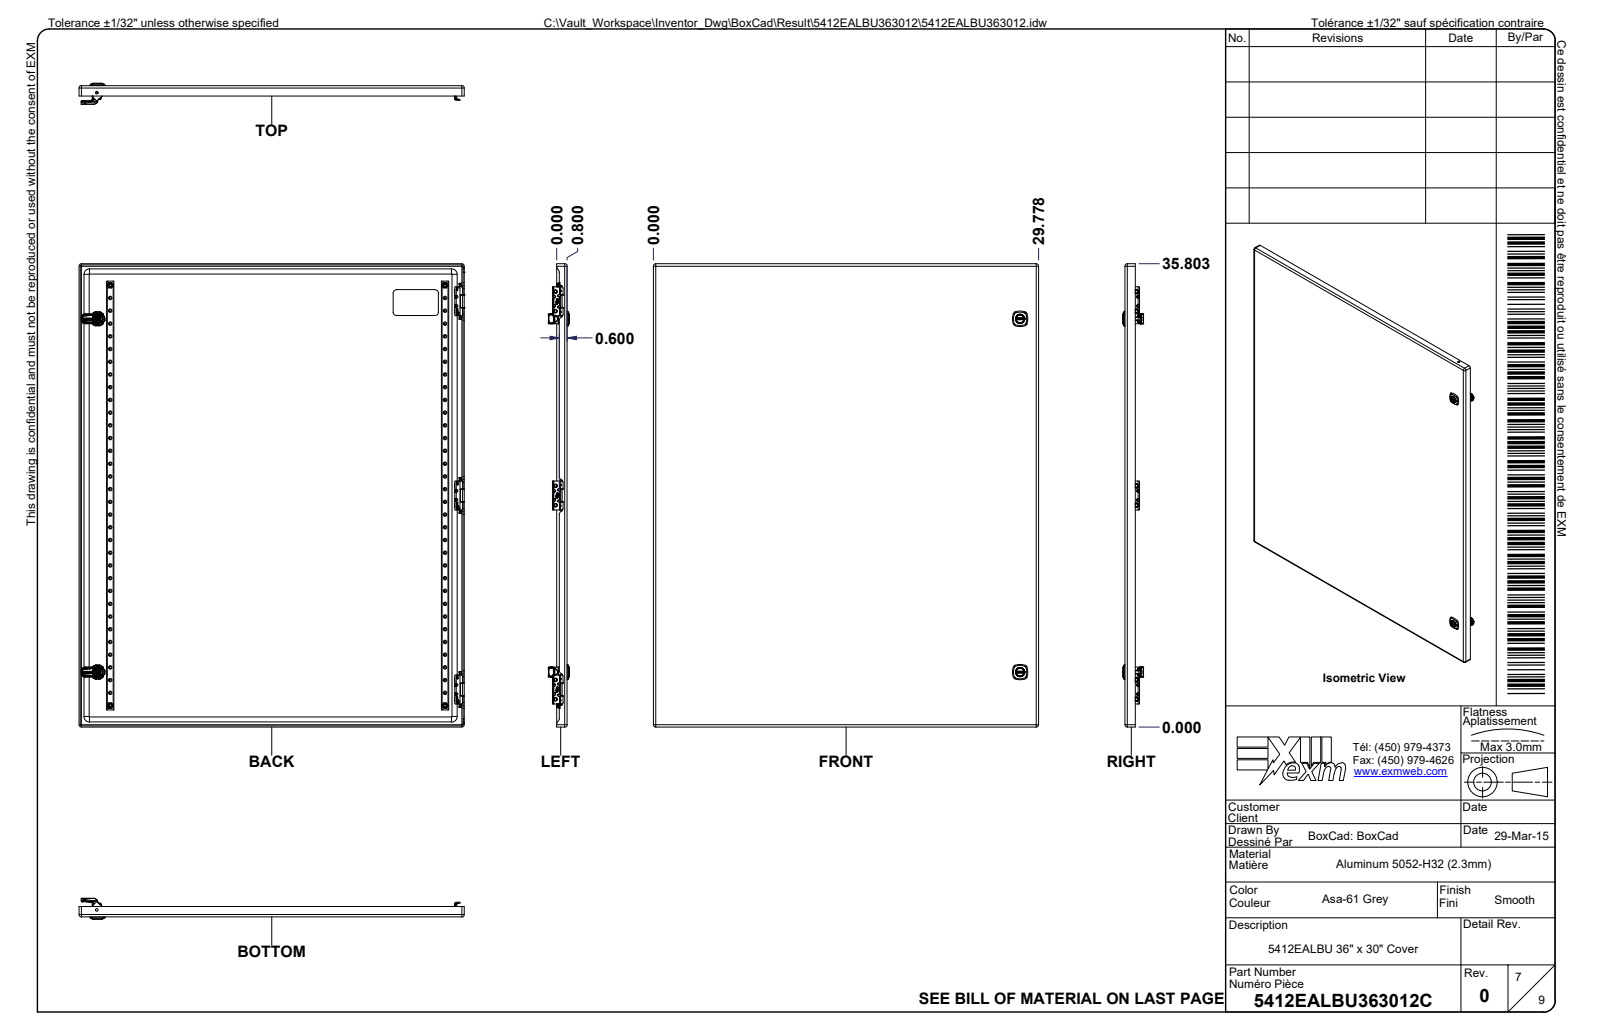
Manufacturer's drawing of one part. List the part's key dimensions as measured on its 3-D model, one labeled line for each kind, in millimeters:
Part name (STEP PRODUCT): 5412EALBU363012; 5412EALBU363012B; 5412EALBU363012B-P; STK-Q-16010 (+8 more)
STEP written by: Autodesk Inventor 2024 (AUTOMOTIVE_DESIGN)
Units: millimetres
Bodies: 87 solids, 7797 faces (3651 planar, 1605 cylindrical, 2541 other)
Overall size (bounding box): 914.4 × 762 × 338.7
Volume: 7 959 000 mm³ · Surface area: 6 833 000 mm²
Round holes (diameter × count): ⌀4.2 ×64, ⌀0.8 ×11, ⌀7.4 ×10, ⌀8 ×8, ⌀1.1 ×6, ⌀4.9 ×6, ⌀5.1 ×6, ⌀6 ×6, ⌀6.9 ×6, ⌀7.9 ×6, ⌀9 ×6, ⌀12.7 ×6
Round bosses / shafts (diameter × count): ⌀6 ×64, ⌀5.9 ×13, ⌀1 ×12, ⌀0.8 ×11, ⌀12 ×6, ⌀9 ×6, ⌀7.9 ×6, ⌀6.4 ×6
Partial cylindrical surfaces — rounded edges, fillets, slot ends (radius × count): R0.2 ×140, R0.5 ×106, R1 ×94, R0.3 ×50, R0.8 ×39, R3.2 ×31, R0.3 ×28, R3.1 ×25
Main face-to-face distances: 2.3, 332, 329.7, 334.3, 24.5, 22.2, 307.5, 309.8, 27.2, 24.9
Hole centre spacings: 25, 50, 75, 100, 125, 150, 175, 200
